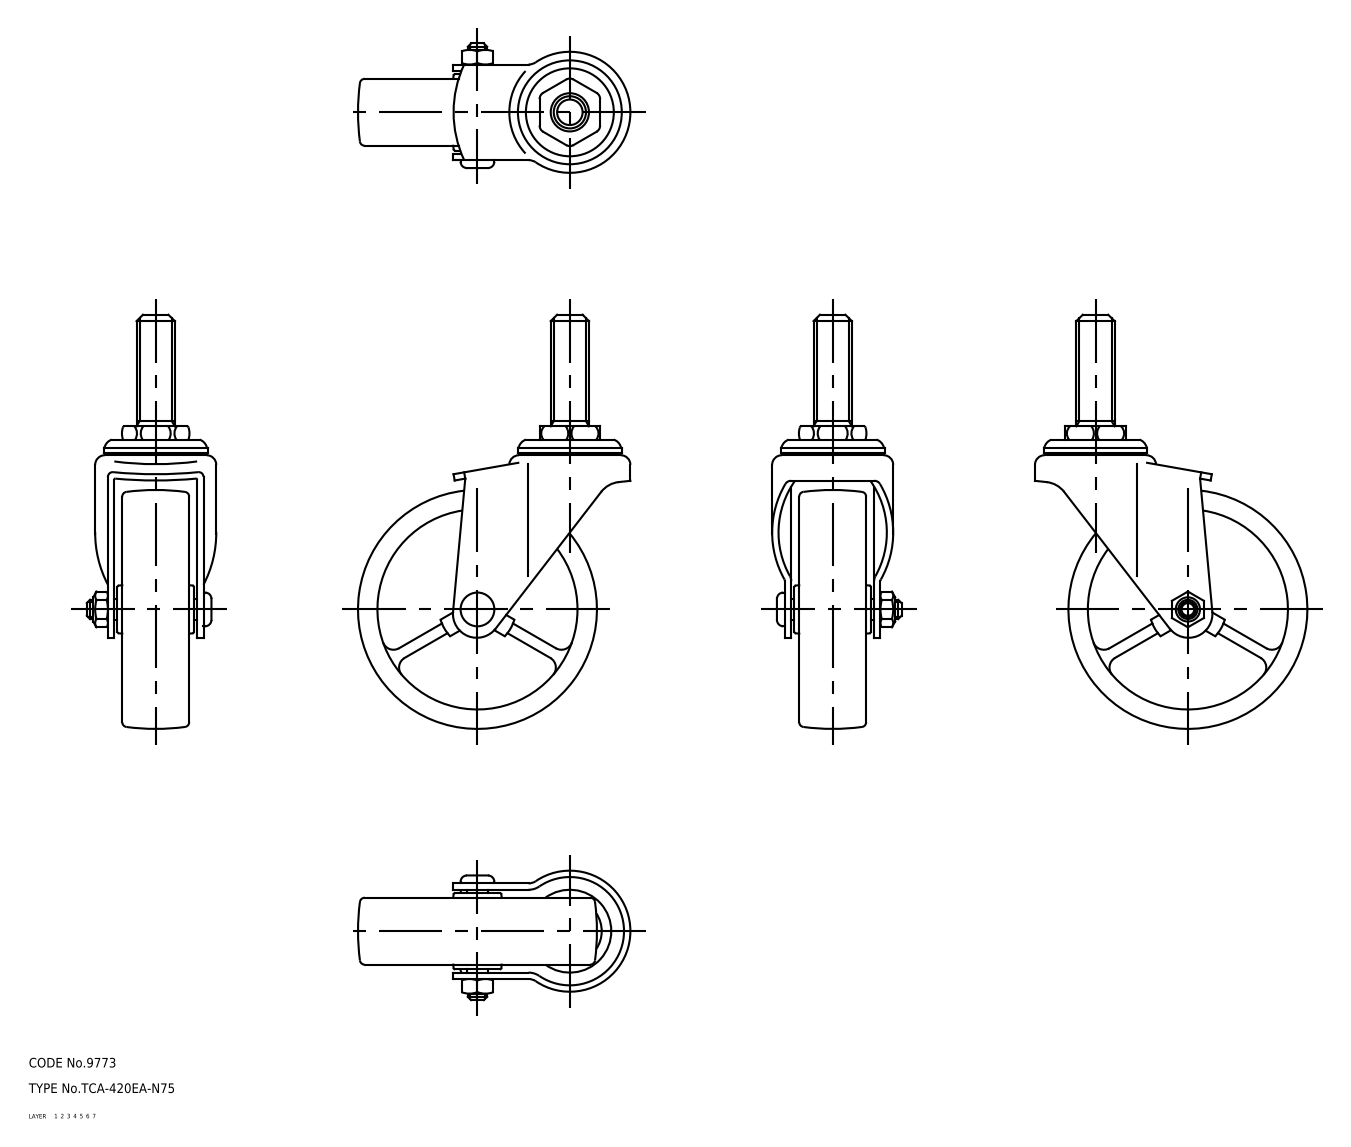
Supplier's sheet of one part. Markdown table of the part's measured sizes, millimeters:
| quantity | value |
| --- | --- |
| part name | wheel; mounting plate; main shaft; axle (+1 more) |
| STEP written by | CADfix (AUTOMOTIVE_DESIGN) |
| units | millimeters |
| bodies | 5 solids, 404 faces (0 planar, 0 cylindrical, 404 other) |
| overall size | 130 × 85.5 × 40.6 |
| volume | 87 715 mm³ |
| surface area | 34 197 mm² |
